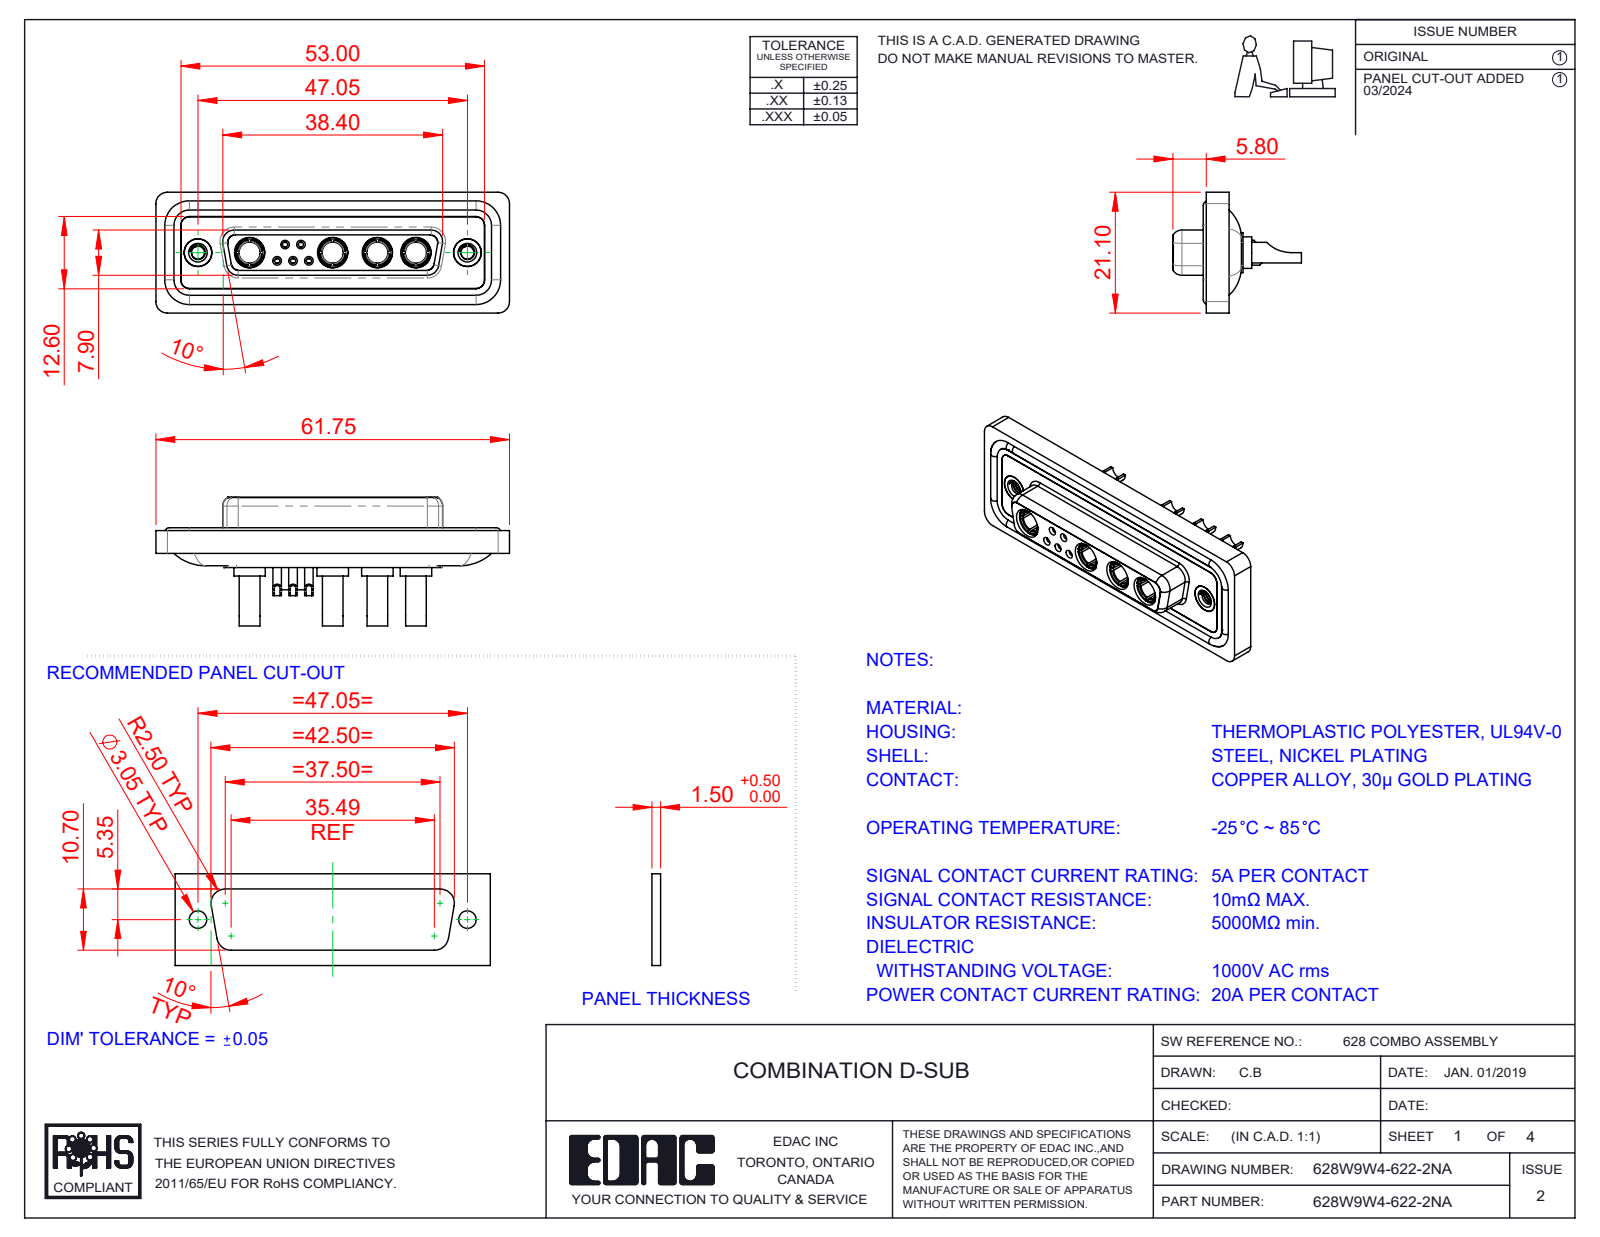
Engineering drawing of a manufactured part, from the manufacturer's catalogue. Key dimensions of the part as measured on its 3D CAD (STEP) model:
Part name (STEP PRODUCT): 628Combo Housing_9W4; 628Combo Threaded Rivet_A; Power Socket_20A SC; 628Combo Shell Front_25 Contacts (+5 more)
STEP written by: SolidWorks 2023 (CONFIG_CONTROL_DESIGN)
Units: millimetres
Bodies: 20 solids, 979 faces (318 planar, 399 cylindrical, 262 other)
Overall size (bounding box): 61.75 × 22.45 × 21.1
Volume: 8 287 mm³ · Surface area: 13 944 mm²
Round holes (diameter × count): ⌀4.85 ×6, ⌀0.9 ×5, ⌀1 ×5, ⌀1.1 ×5, ⌀1.5 ×5, ⌀2 ×5, ⌀2.7 ×4, ⌀3.7 ×4, ⌀5.3 ×4, ⌀1.6 ×3, ⌀1.7 ×2, ⌀2.26 ×2
Round bosses / shafts (diameter × count): ⌀1.6 ×6, ⌀2.2 ×5, ⌀5.5 ×4, ⌀5.2 ×4, ⌀4.96 ×4, ⌀4.75 ×4, ⌀3.75 ×4, ⌀3.6 ×4
Partial cylindrical surfaces — rounded edges, fillets, slot ends (radius × count): R1.5 ×22, R2 ×18, R1.35 ×8, R1.6 ×8, R1 ×6, R0.25 ×4, R0.5 ×4, R0.6 ×4
Main face-to-face distances: 0.4, 1.8, 7.45, 5.65, 0.5, 7.05, 6.6, 1.6, 1.1, 2.9
Hole centre spacings: 3.16, 2.77, 5.03, 2.76, 4.4, 5.02, 5.54, 5.73
